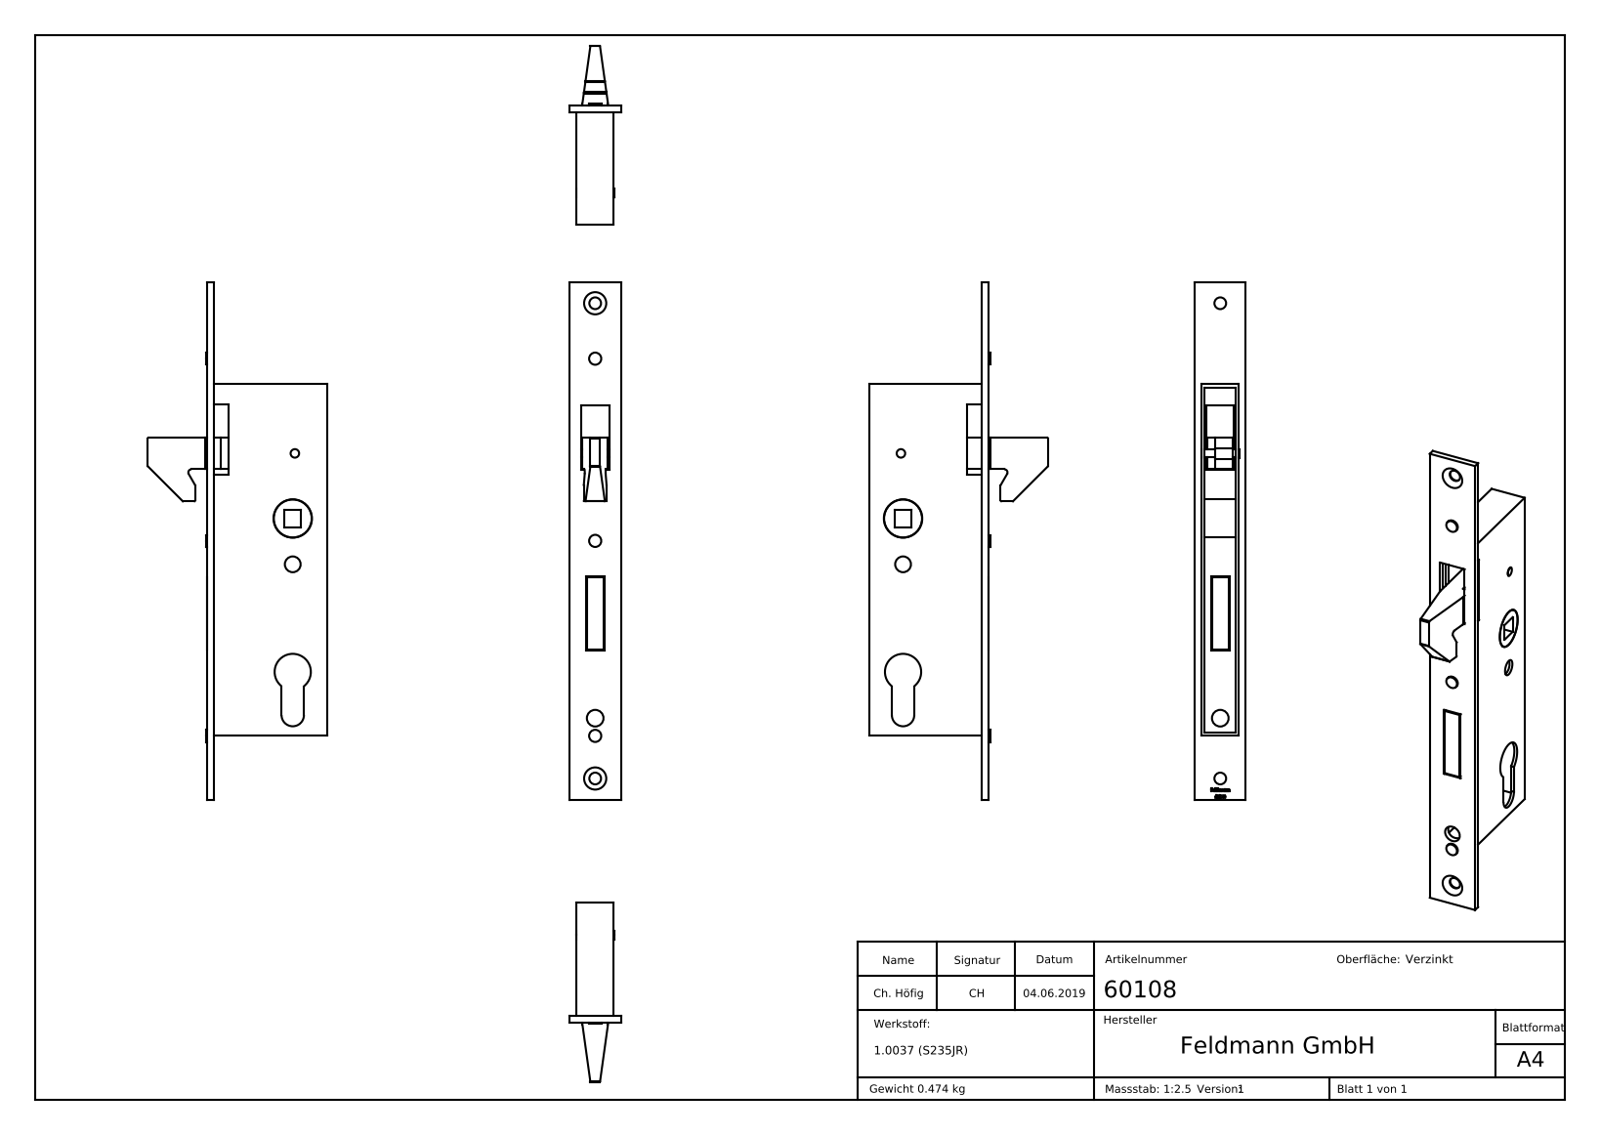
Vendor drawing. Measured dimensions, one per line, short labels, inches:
name: 60108
written by: SolidWorks 2015 (CONFIG_CONTROL_DESIGN)
unit: in
bodies: 5 solids, 291 faces (152 planar, 43 cylindrical, 96 other)
size: 9.567 × 3.307 × 0.945
volume: 3.711 in³; area: 87.24 in²
holes: 2× ⌀0.217, 1× ⌀0.291, 1× ⌀0.307, 1× ⌀0.709
bosses: 3× ⌀0.224, 1× ⌀0.701, 1× ⌀0.157, 1× ⌀0.15
rounds: 5× R0.02, 1× R0.059, 1× R0.207, 1× R0.335
face distances: 0.059, 0.63, 0.571, 0.689, 0.118, 0.187, 6.437, 0.128, 0.758, 0.817
hole spacings: 0.846, 1.114, 7.665, 8.78
